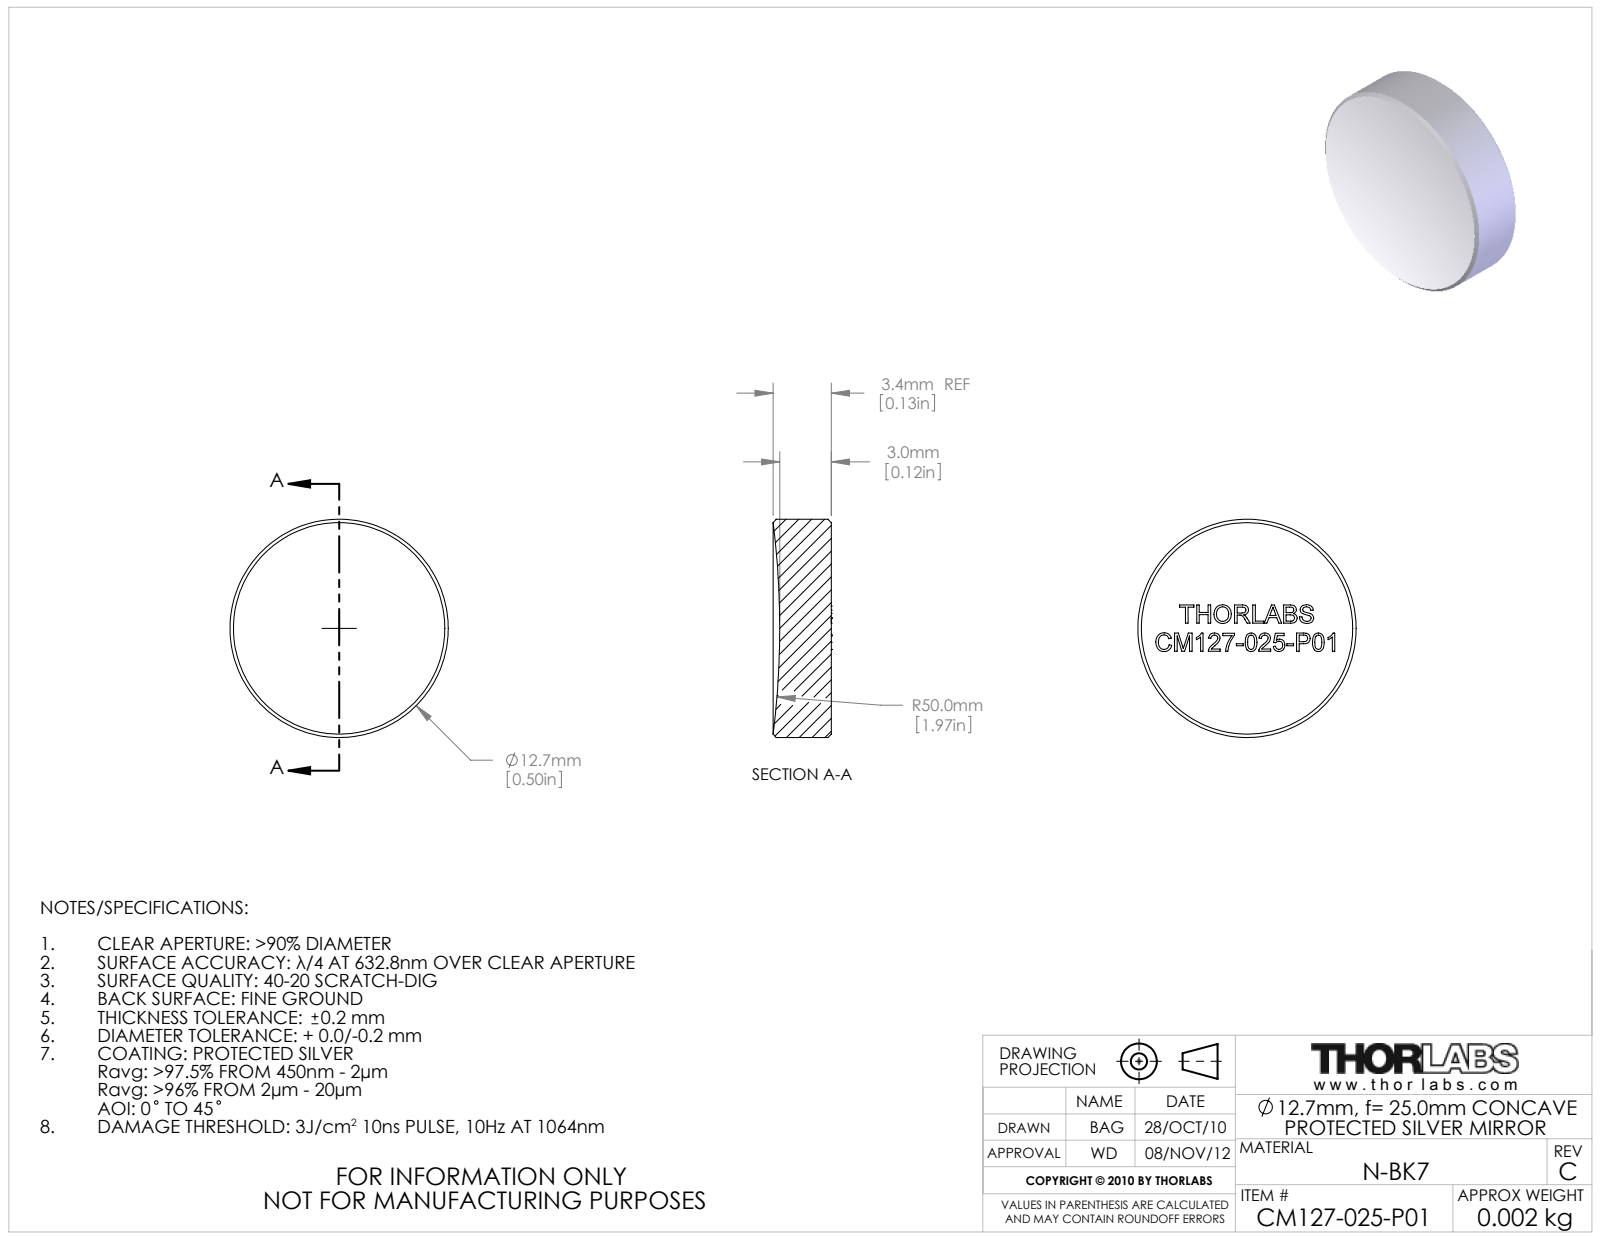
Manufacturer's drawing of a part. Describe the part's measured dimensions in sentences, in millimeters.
The part is named "17565-E0W". Its 3-D file was written by "SolidWorks 2009 (AUTOMOTIVE_DESIGN)". It is 1 solid with 270 faces: 150 planar, 2 cylindrical and 118 other. Overall it measures 12.7 by 12.7 by 3.4 millimeters. Its volume is 410 cubic millimeters and its surface area 379 square millimeters. Round bosses or shafts: 1 of diameter 12.7. The main face-to-face distances are 1.1, 1.3, 1.6, 0.9, 0.9, 0.6, 0.9, 0.7, 1, 0.5.
